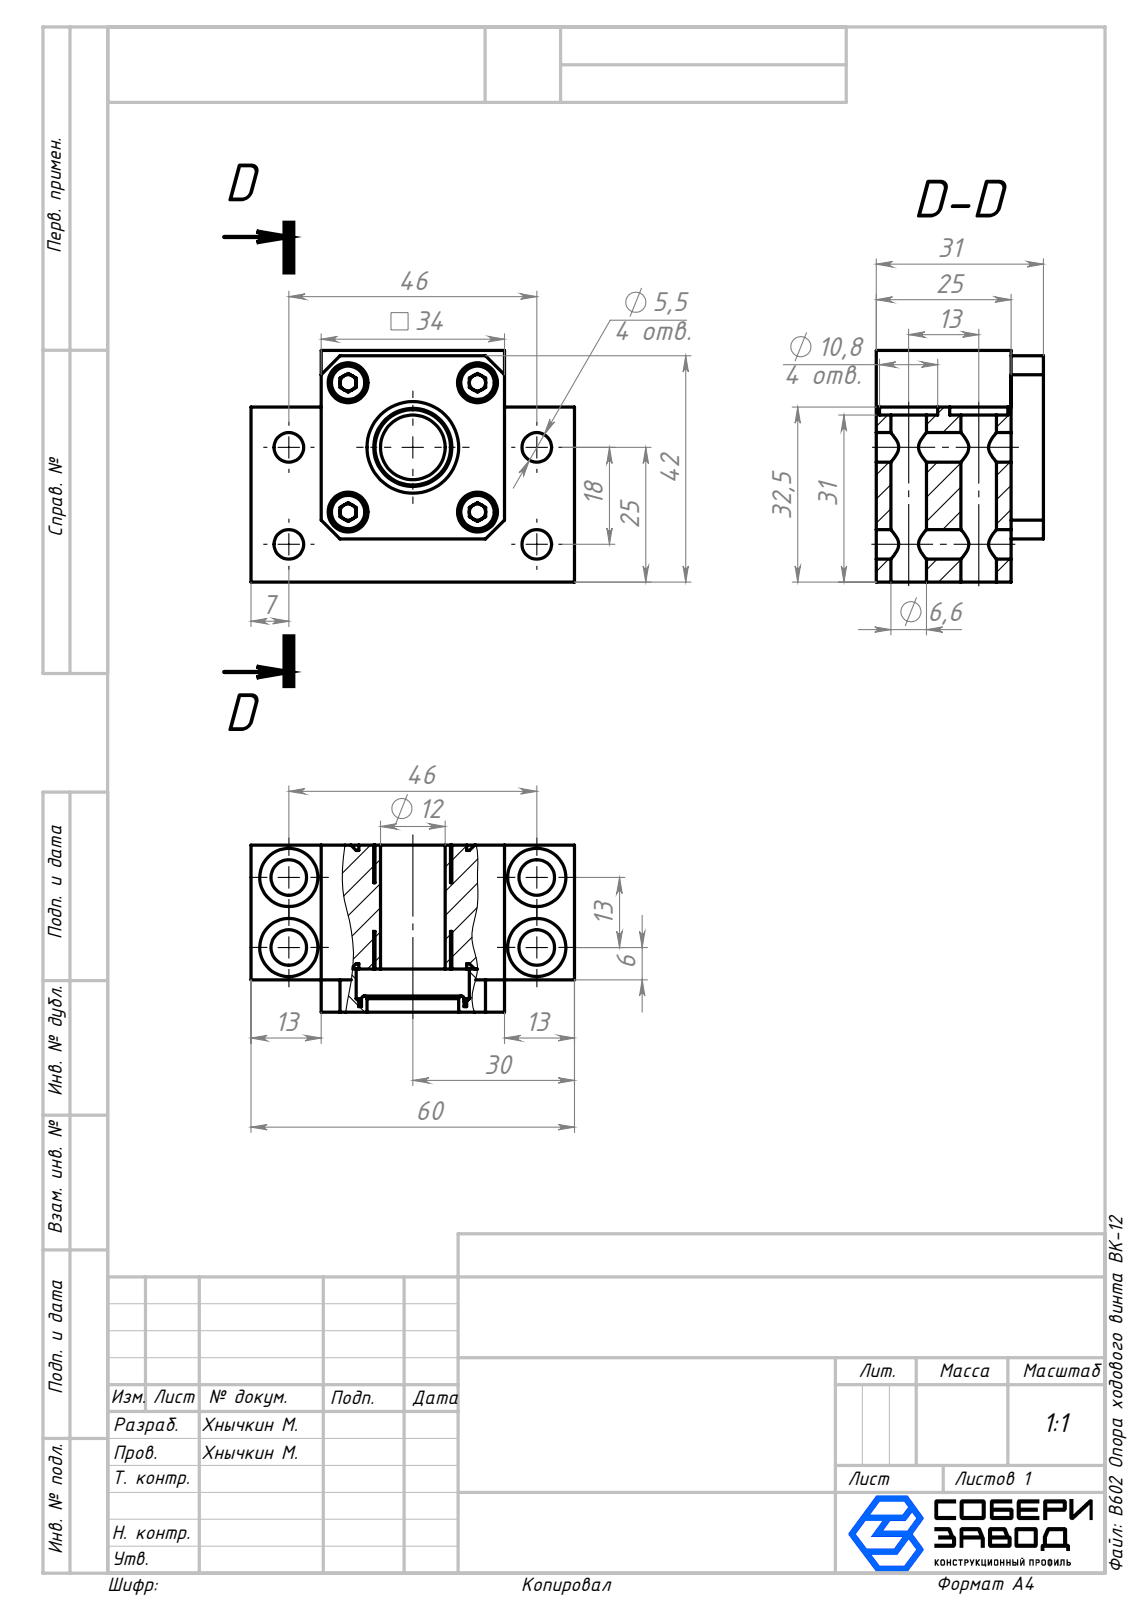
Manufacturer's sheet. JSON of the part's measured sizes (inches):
{"part_name": "B602 Крышка_00; socket head cap screw_din_DIN 912 M4 x 6 --- 6N; B602 Опора ходового винта BK-12; B602 Опора ходового винта BK-12-корпус_00", "step_written_by": "SolidWorks 2026 (AUTOMOTIVE_DESIGN)", "units": "inches", "bodies": {"solids": 6, "faces": 251, "planar": 103, "cylindrical": 106, "other": 42}, "overall_size": [2.362, 1.693, 1.22], "volume_in3": 3.227, "surface_area_in2": 30.89, "round_holes": [[0.118, 4], [0.177, 4], [0.217, 4], [0.26, 4], [0.291, 4], [0.425, 4], [0.472, 1], [0.571, 1], [0.669, 1], [0.827, 1], [1.024, 1]], "round_bosses_or_shafts": [[0.276, 4], [0.157, 4], [0.787, 1], [0.748, 1], [0.551, 1]], "face_to_face_distances": [0.984, 1.22, 0.236, 0.512, 1.693, 1.85, 2.362, 0.079, 0.315, 0.906], "hole_center_spacings": [0.641, 0.668, 0.945, 1.457, 1.811, 0.493, 0.512, 0.709]}
